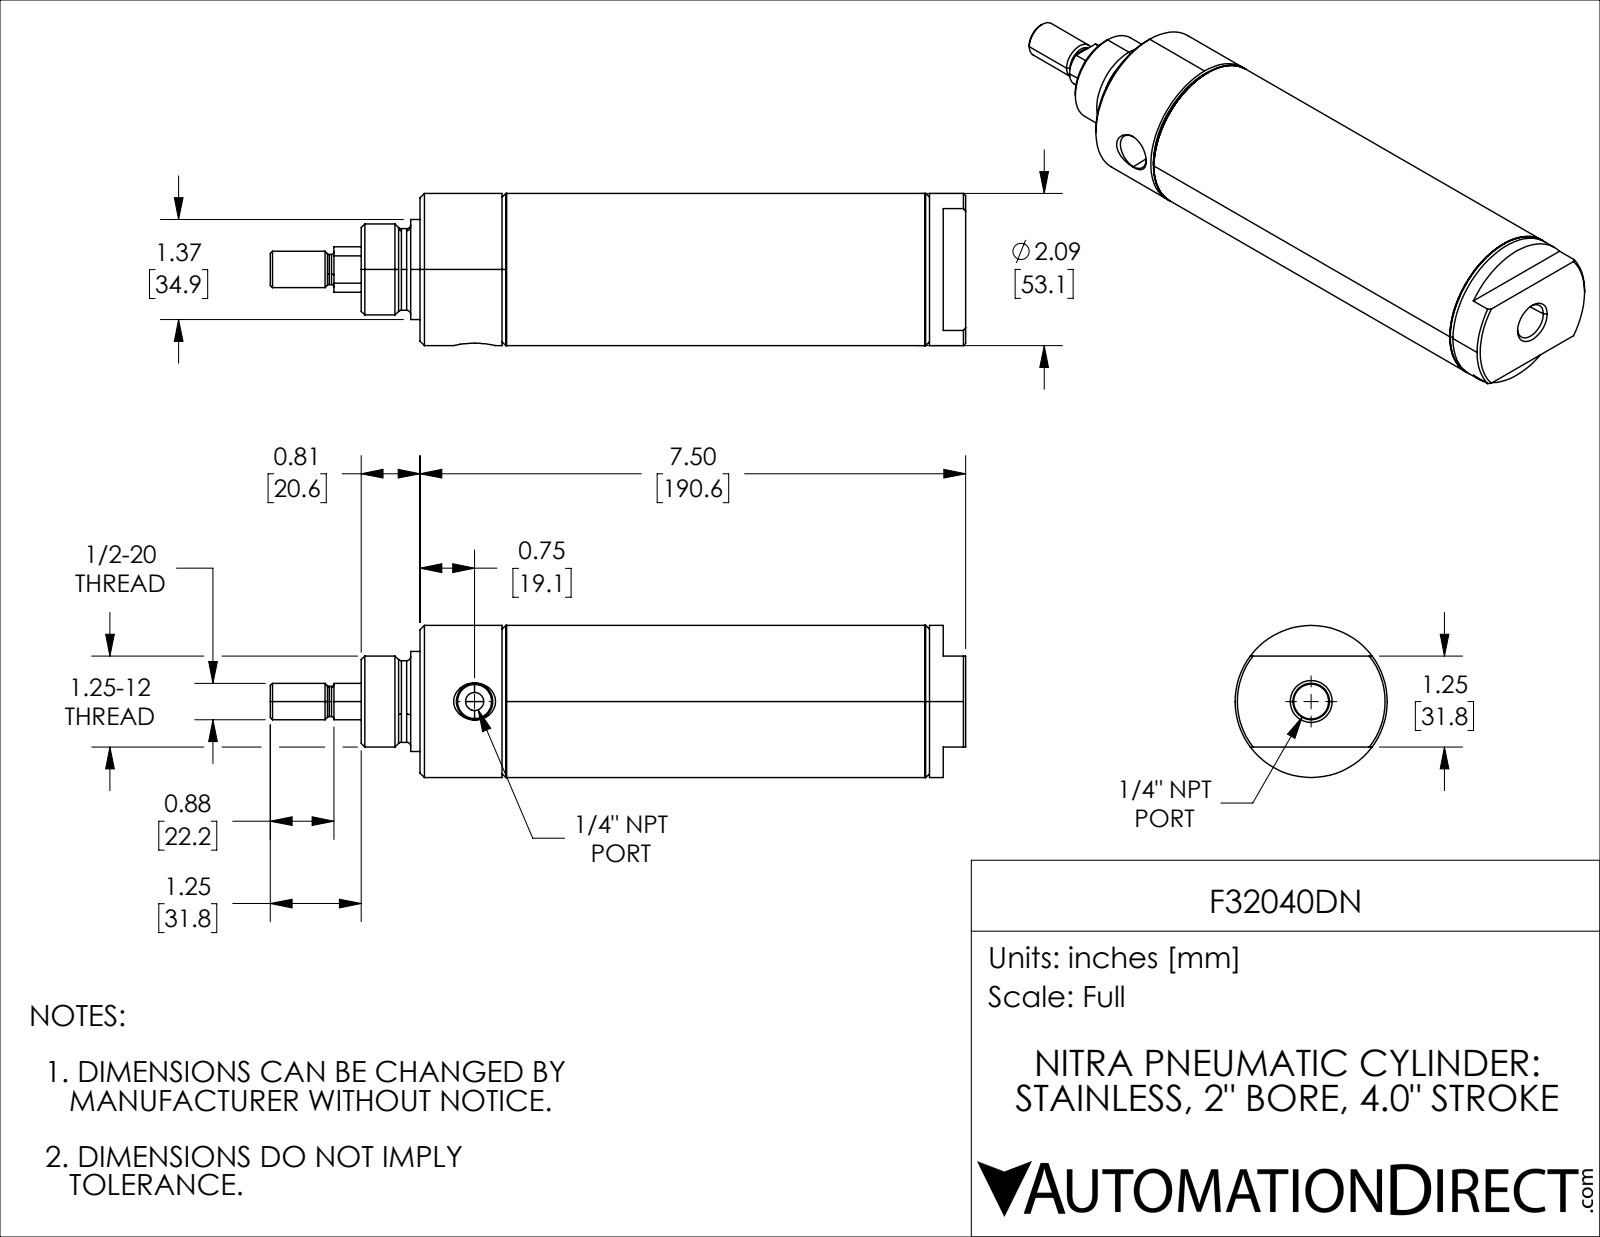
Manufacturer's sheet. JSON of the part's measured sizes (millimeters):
{"part_name": "F32040DN_5; F32040DN; F32040DN_9; F32040DN_7 (+1 more)", "step_written_by": "SolidWorks 2021 (CONFIG_CONTROL_DESIGN)", "units": "millimeters", "bodies": {"solids": 4, "faces": 133, "planar": 25, "cylindrical": 46, "other": 62}, "overall_size": [242.88, 53.09, 53.09], "volume_mm3": 237153, "surface_area_mm2": 93622, "round_holes": [[6.35, 1], [12.18, 1], [16.52, 1], [31.75, 1], [49.05, 1]], "round_bosses_or_shafts": [[53.09, 1], [51.16, 1], [34.87, 1], [28.51, 1], [15.88, 1], [12.7, 1], [10.46, 1]], "face_to_face_distances": [30.18, 101.6, 131.78, 152.4, 50.8, 20.62, 131.77, 30.17, 20.63, 38.15]}
